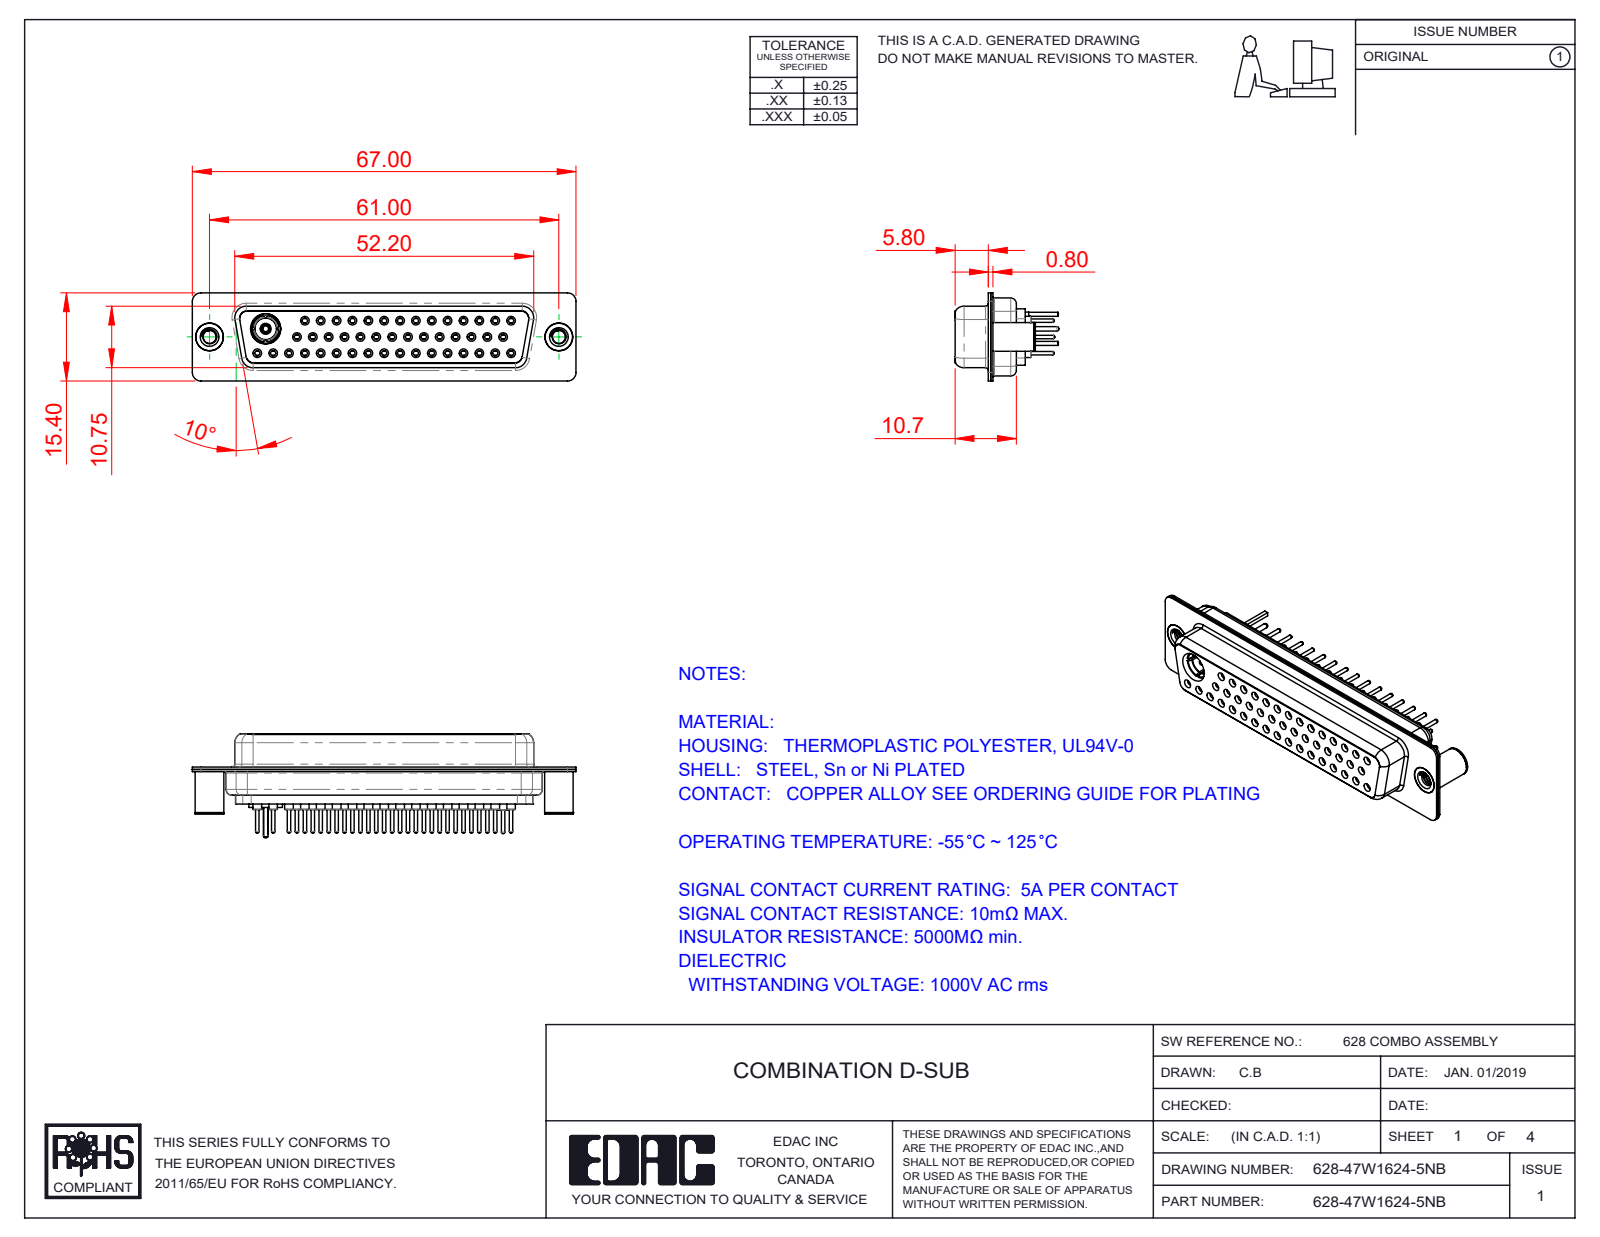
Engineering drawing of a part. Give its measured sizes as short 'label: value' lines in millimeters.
name: Co-Ax Plug_Straight PC Tail; 628Combo Contact Row 2_24; Locking Collar; 628Combo Contact Row 1_24 (+8 more)
written by: SolidWorks 2016 (CONFIG_CONTROL_DESIGN)
unit: mm
bodies: 55 solids, 2965 faces (811 planar, 1080 cylindrical, 1074 other)
size: 67 × 18.15 × 15.4
volume: 7 171 mm³; area: 15 134 mm²
holes: 47× ⌀1.1, 46× ⌀1.5, 45× ⌀0.9, 45× ⌀2, 31× ⌀1.6, 14× ⌀1.7, 3× ⌀4.85, 2× ⌀2.26, 2× ⌀3.26, 2× ⌀4, 2× ⌀4.05, 1× ⌀2.83
bosses: 46× ⌀2.2, 46× ⌀0.6, 15× ⌀1.6, 3× ⌀5, 2× ⌀4.95, 2× ⌀4.8, 1× ⌀5.85, 1× ⌀5.2
rounds: 16× R1.5, 12× R1.35, 12× R2, 8× R1.6, 4× R0.25, 4× R0.5, 4× R0.6, 4× R0.65
face distances: 0.4, 6.05, 6.45, 11.33, 1.87, 12.25, 6.2, 5.8, 10.35, 10.93
hole spacings: 3.16, 2.77, 5.54, 8.31, 11.08, 13.85, 16.62, 19.39
